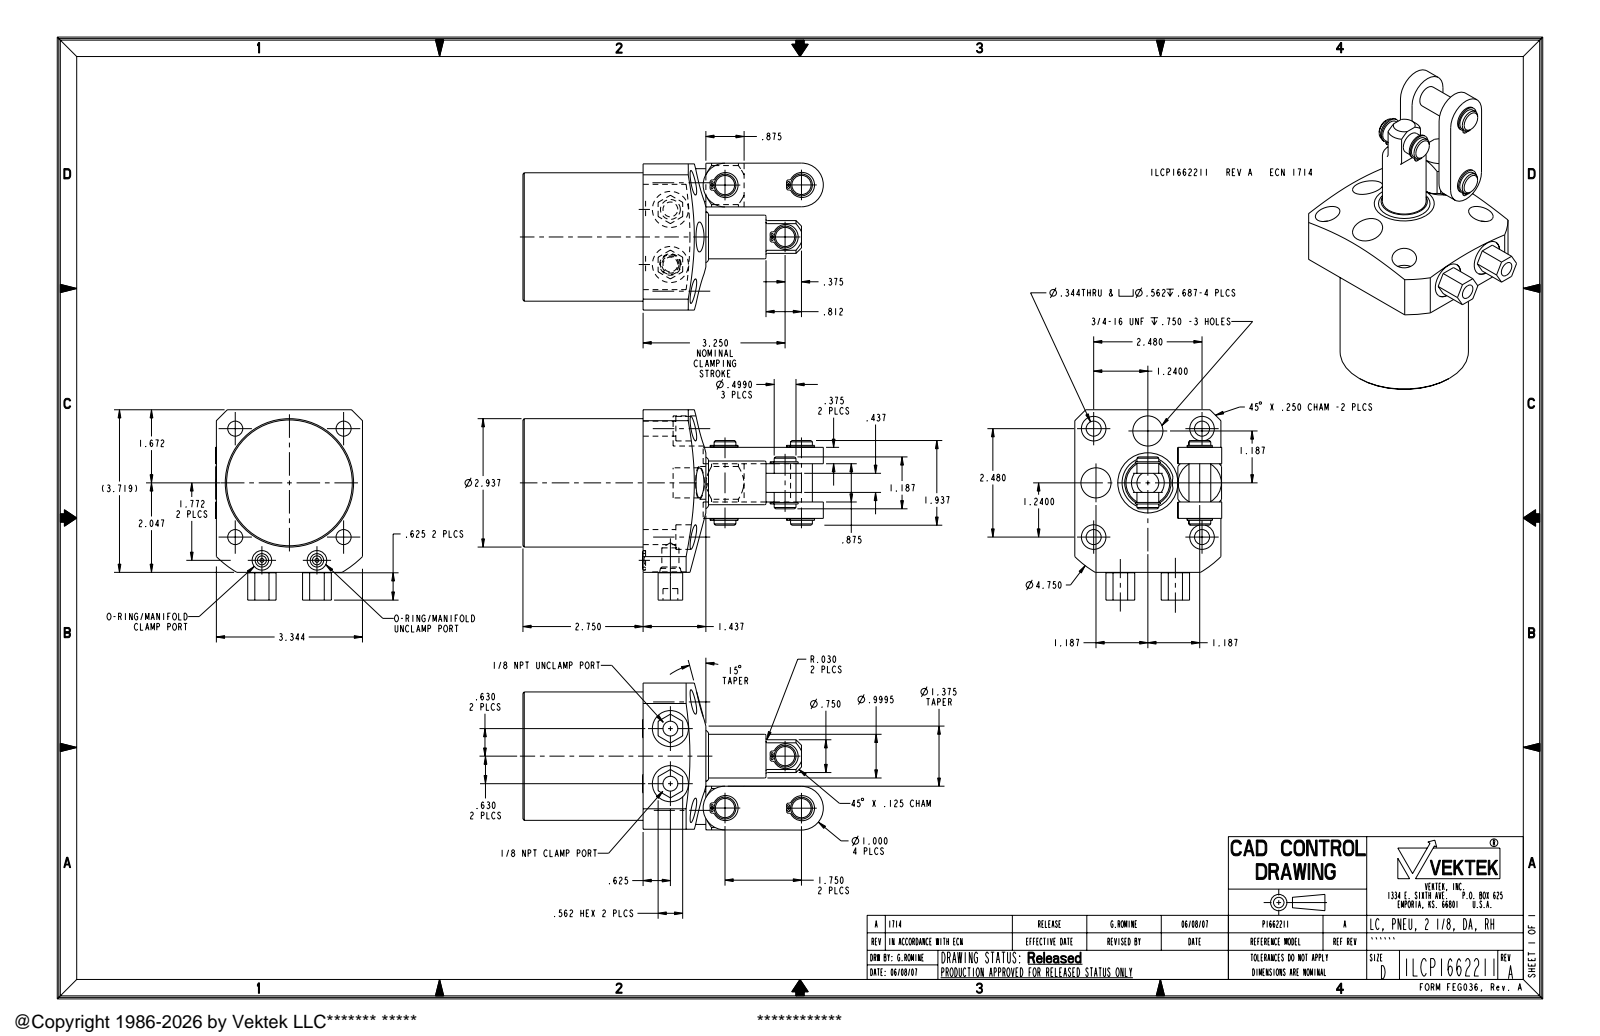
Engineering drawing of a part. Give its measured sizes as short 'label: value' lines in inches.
name: ILCP1662211
written by: PRO/ENGINEER BY PARAMETRIC TECHNOLOGY CORPORATION, 2005180 (AUTOMOTIVE_DESIGN_CC2)
unit: in
bodies: 3 solids, 301 faces (120 planar, 133 cylindrical, 48 other)
size: 6.875 × 4.354 × 3.362
volume: 37.44 in³; area: 105.7 in²
holes: 6× ⌀0.047, 4× ⌀0.344, 4× ⌀0.562, 2× ⌀0.339, 2× ⌀0.392, 2× ⌀0.447, 2× ⌀0.689, 2× ⌀0.825
bosses: 3× ⌀0.574, 3× ⌀0.499, 2× ⌀0.437, 1× ⌀2.937, 1× ⌀1, 1× ⌀0.75
rounds: 12× R0.047, 2× R0.5, 1× R0.375, 1× R0.625, 1× R2.375
face distances: 2.75, 0.375, 3.344, 1.25, 0.875, 2.485, 0.859, 1.625, 1, 0.75
hole spacings: 1.241, 2.48, 2.726, 0.113, 0.809, 1.26, 1.75, 1.816
